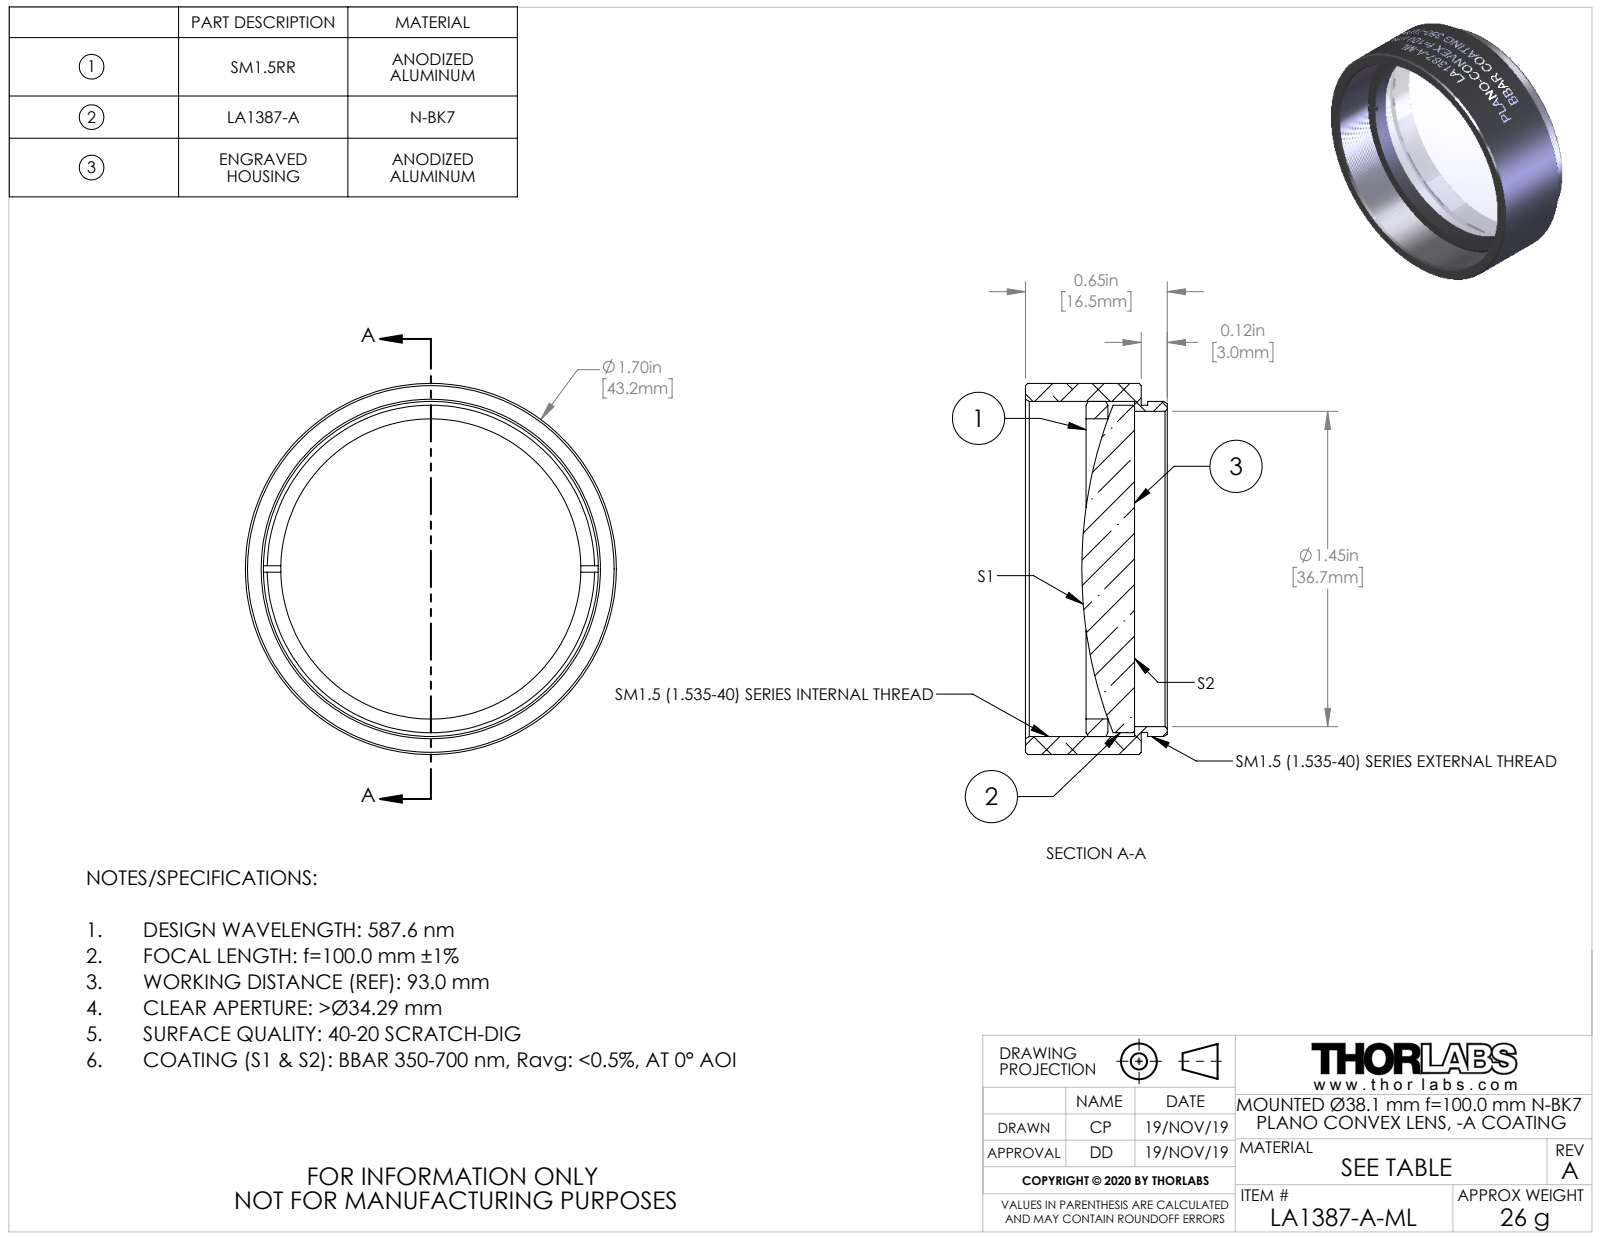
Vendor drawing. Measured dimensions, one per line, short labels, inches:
name: TTN200722-E0W
written by: SolidWorks 2018 (CONFIG_CONTROL_DESIGN)
unit: in
bodies: 3 solids, 157 faces (15 planar, 123 cylindrical, 19 other)
size: 1.7 × 1.7 × 0.65
volume: 0.587 in³; area: 13.39 in²
holes: 1× ⌀1.375, 1× ⌀1.445
bosses: 1× ⌀1.7, 1× ⌀1.535, 1× ⌀1.5, 1× ⌀1.499
face distances: 0.03, 0.53, 0.5, 0.152, 0.122, 0.378, 0.252, 0.222, 0.1, 0.278
